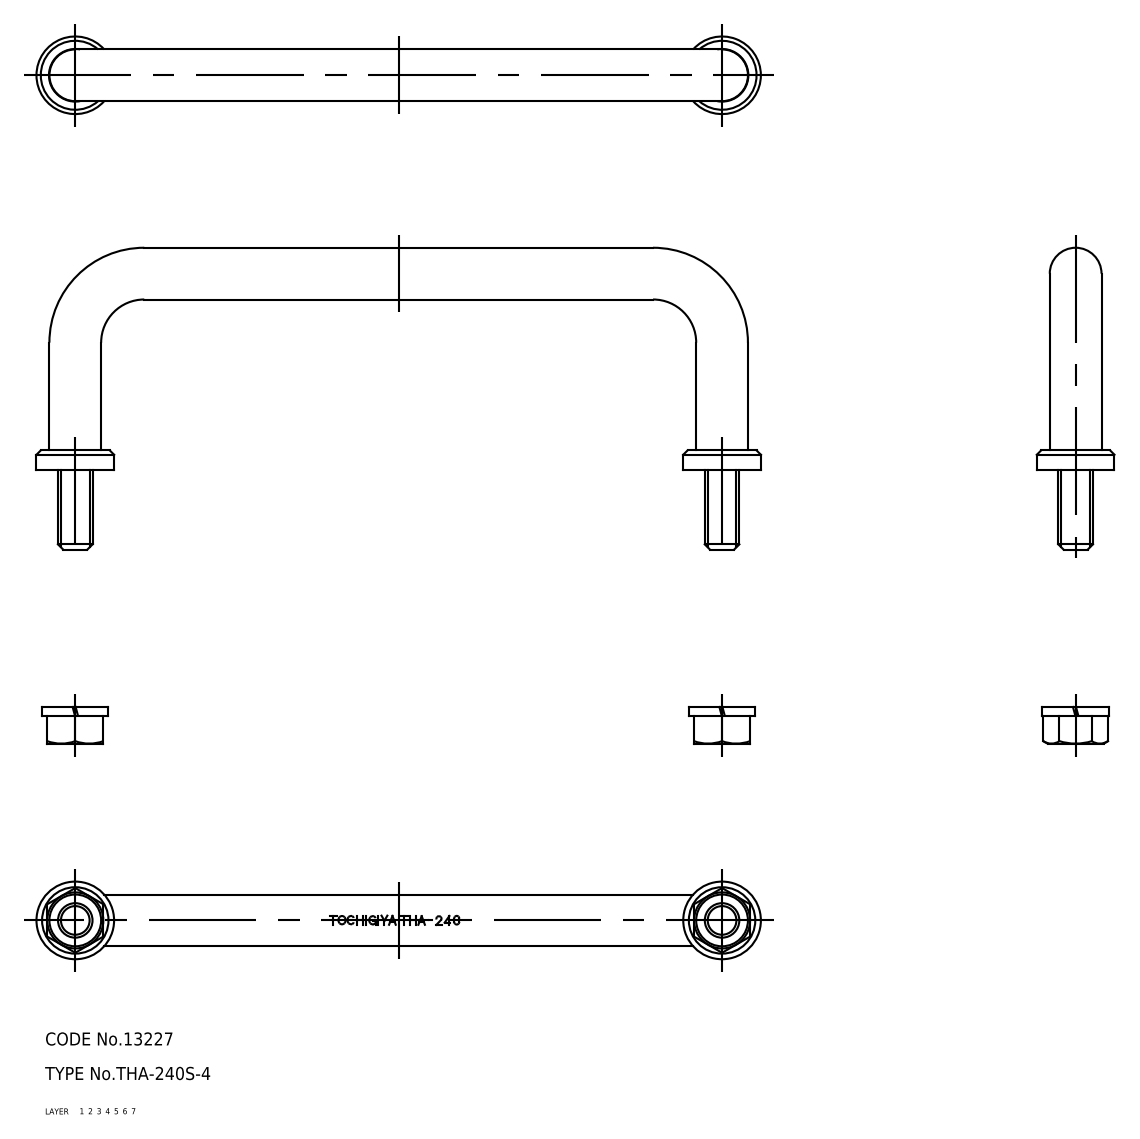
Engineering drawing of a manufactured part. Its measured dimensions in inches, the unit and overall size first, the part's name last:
Units: inches
Overall size (bounding box): 6.614 × 2.756 × 0.709
Volume: 1.872 in³ · Surface area: 20.63 in²
Bodies: 7 solids, 86 faces (0 planar, 0 cylindrical, 86 other)
Part name (STEP PRODUCT): facing ring; nut; washer; pull (+1 more)
STEP written by: CADfix (AUTOMOTIVE_DESIGN)
